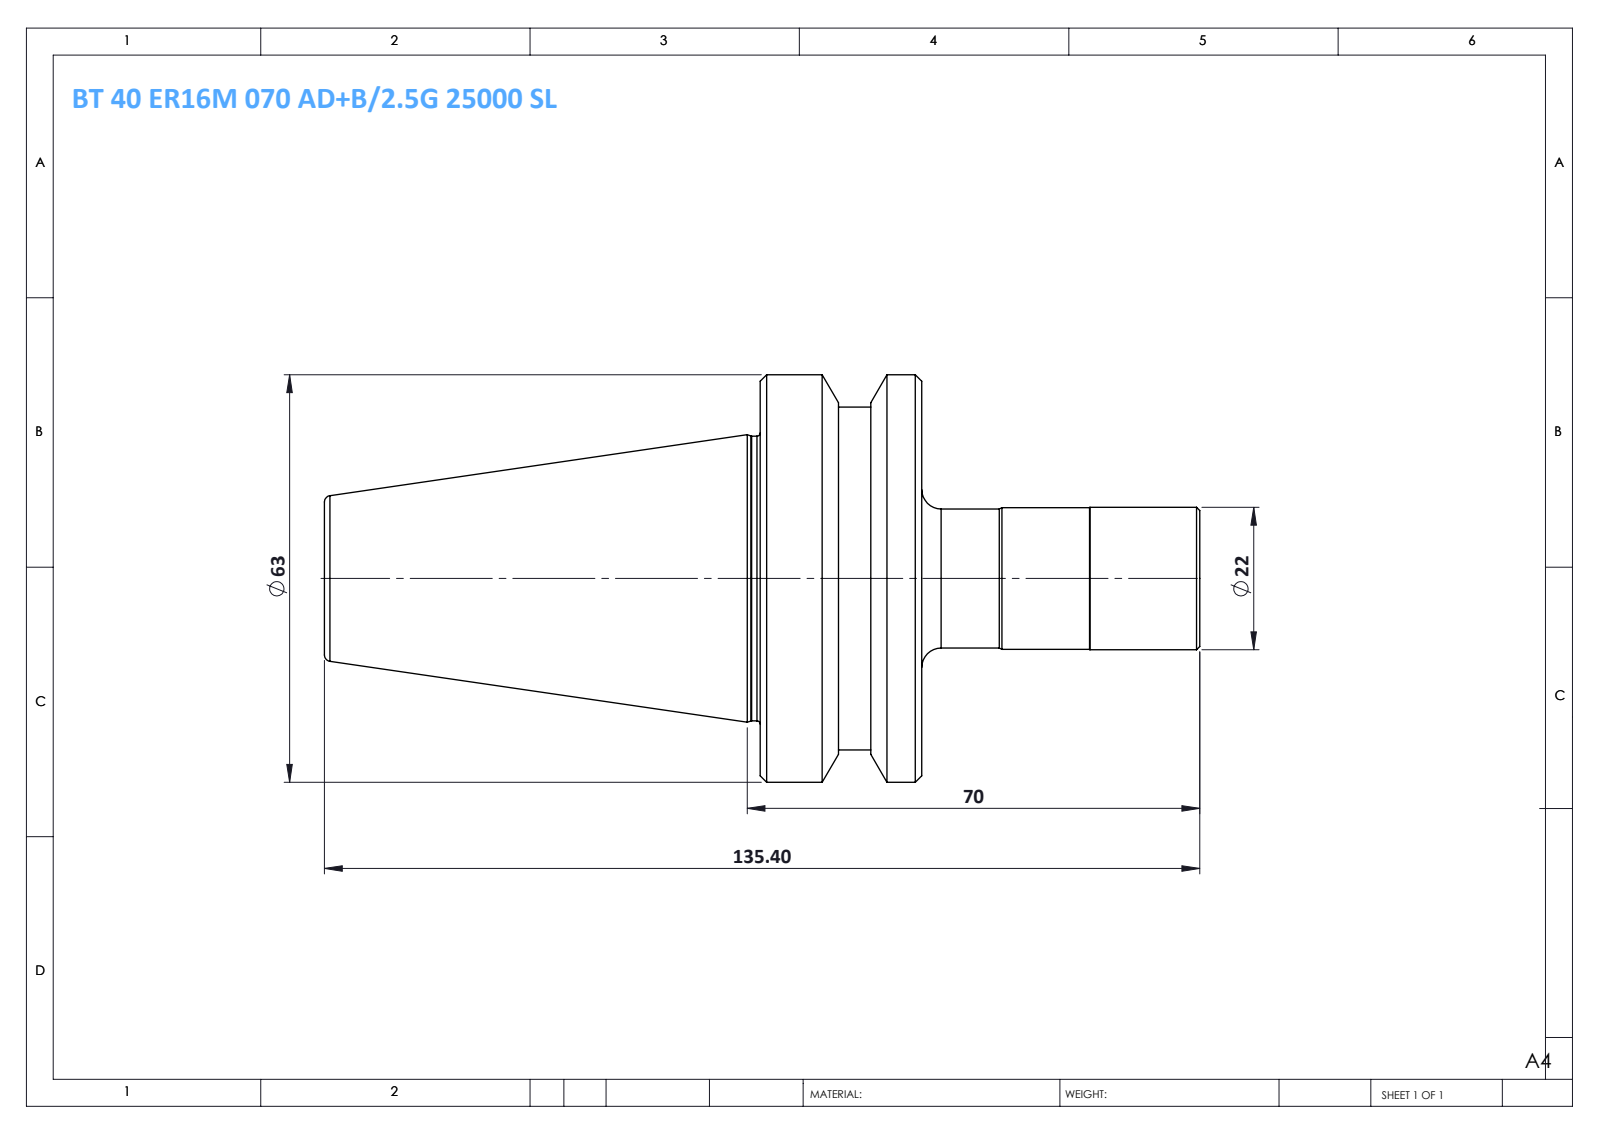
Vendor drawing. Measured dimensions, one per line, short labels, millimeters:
name: BT 40 ER16M 070 AD+B-2.5G 25000 SL
written by: SolidWorks 2014 (CONFIG_CONTROL_DESIGN)
unit: mm
bodies: 1 solid, 46 faces (6 planar, 14 cylindrical, 26 other)
size: 135.4 × 63 × 63
volume: 154 568 mm³; area: 21 199 mm²
bosses: 1× ⌀63, 1× ⌀53, 1× ⌀44, 1× ⌀22, 1× ⌀21.9, 1× ⌀21.5
face distances: 25, 92.4, 67.4, 43, 68, 135.4, 55.9, 12.9, 12.1, 79.5
